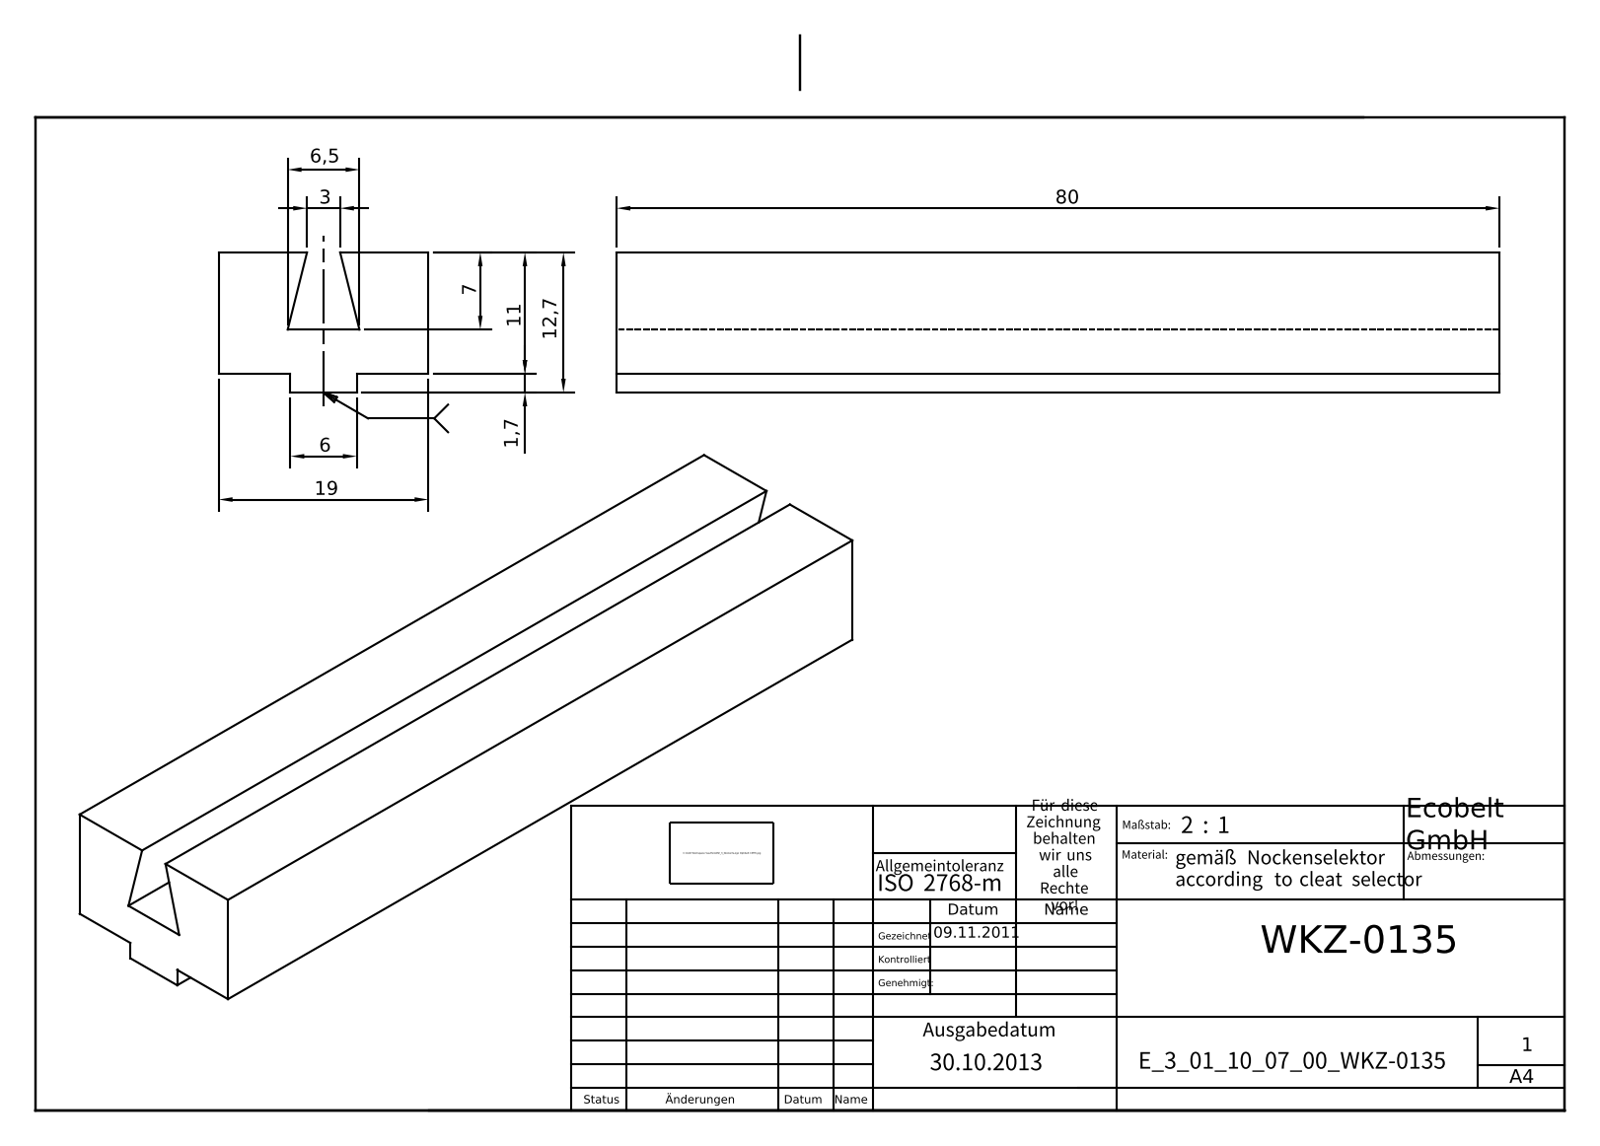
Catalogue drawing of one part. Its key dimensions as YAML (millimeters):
part_name: "E_3_01_10_07_00_WKZ-0135"
step_written_by: "Autodesk Inventor 2025 (AUTOMOTIVE_DESIGN)"
units: millimeters
bodies: {solids: 1, faces: 14, planar: 14, cylindrical: 0, other: 0}
overall_size: [80, 19, 12.7]
volume: 14876
surface_area: 6878
face_to_face_distances: [11, 19, 4, 7, 1.7, 5.7, 12.7, 6.5, 12.5, 80]
